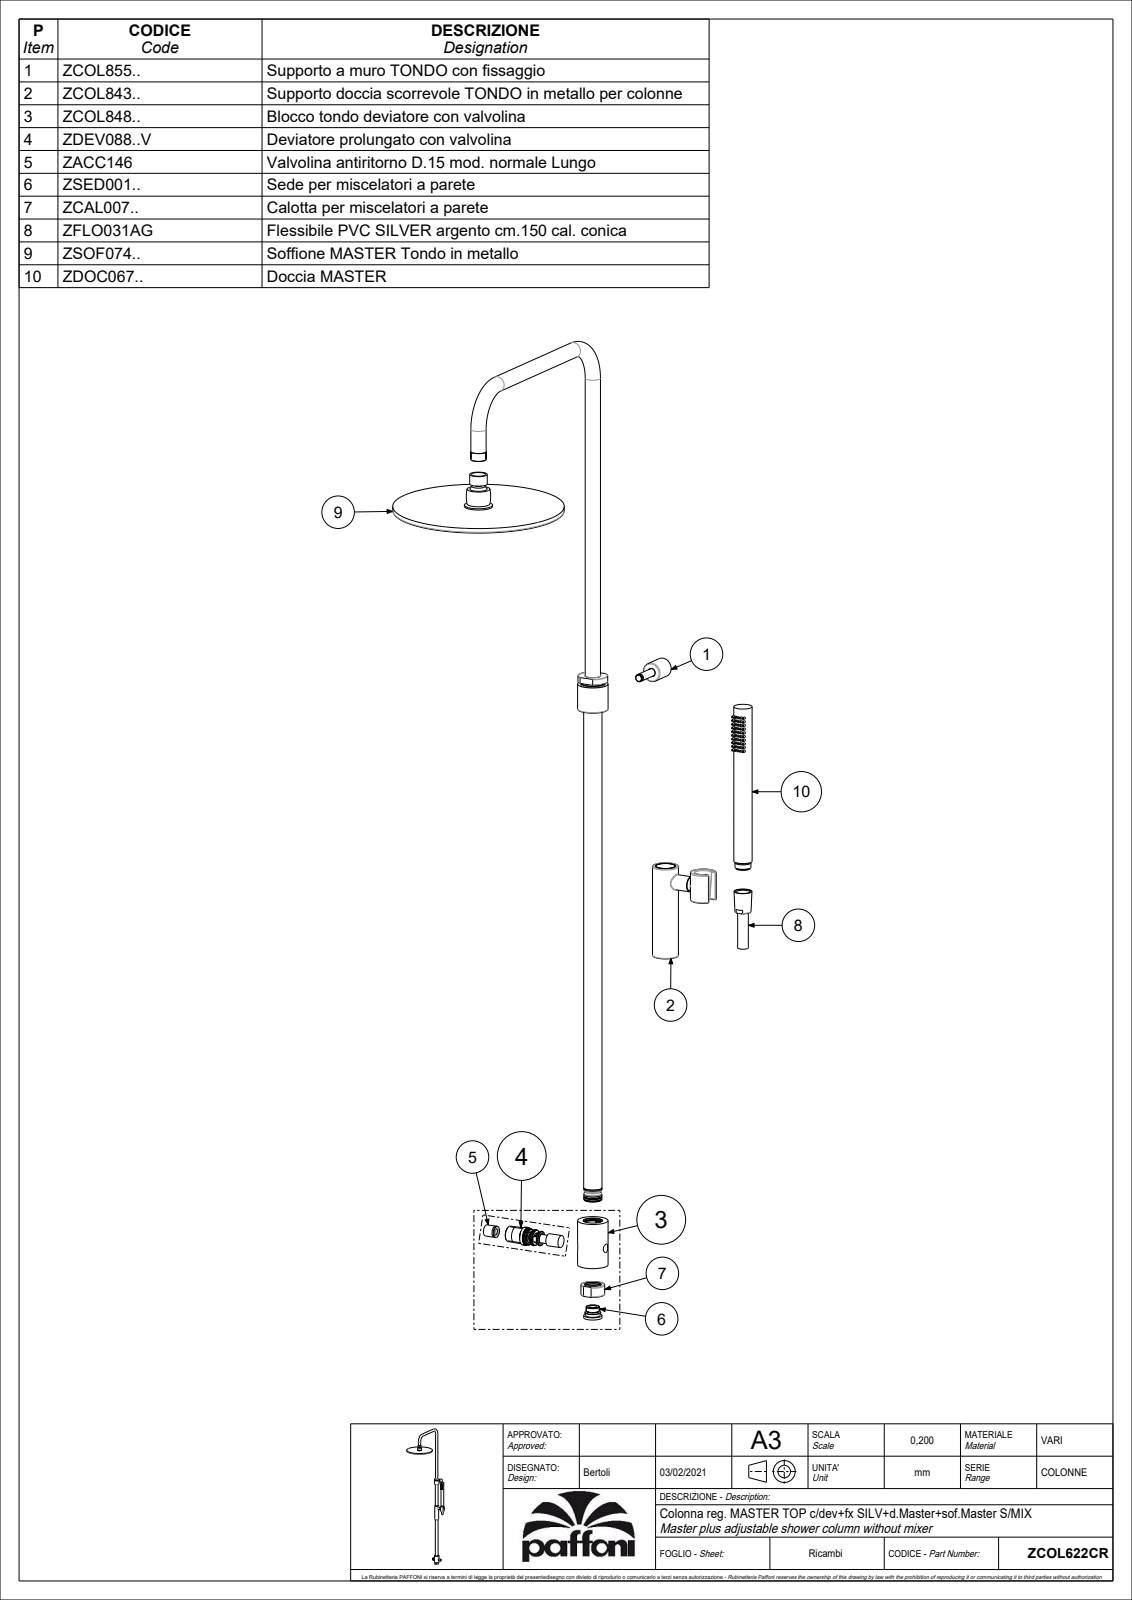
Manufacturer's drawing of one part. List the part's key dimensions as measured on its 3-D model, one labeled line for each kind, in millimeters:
Part name (STEP PRODUCT): ZCOL622CR
STEP written by: CREO PARAMETRIC BY PTC INC, 2020044 (CONFIG_CONTROL_DESIGN)
Units: millimetres
Bodies: 31 solids, 1521 faces (554 planar, 509 cylindrical, 458 other)
Overall size (bounding box): 1235 × 491.3 × 225
Volume: 650 952 mm³ · Surface area: 422 985 mm²
Round holes (diameter × count): ⌀1.2 ×80, ⌀1 ×50, ⌀5 ×4, ⌀17 ×4, ⌀10 ×3, ⌀3.3 ×2, ⌀3.5 ×2, ⌀10.5 ×2, ⌀12 ×2, ⌀25 ×2, ⌀27 ×2, ⌀4.2 ×1
Round bosses / shafts (diameter × count): ⌀20 ×4, ⌀24 ×2, ⌀225 ×1, ⌀40 ×1, ⌀37 ×1, ⌀34 ×1, ⌀29.8 ×1, ⌀28 ×1
Partial cylindrical surfaces — rounded edges, fillets, slot ends (radius × count): R0.3 ×24, R1 ×6, R6.75 ×1, R12.1 ×1, R12.3 ×1, R12.32 ×1, R15.6 ×1, R17 ×1
Main face-to-face distances: 6.5, 8, 1078.5, 1085, 236.75, 46, 38, 331, 60, 1018.5
Hole centre spacings: 6.4, 4, 28.16, 90, 9.43, 8, 10.77, 81.72
